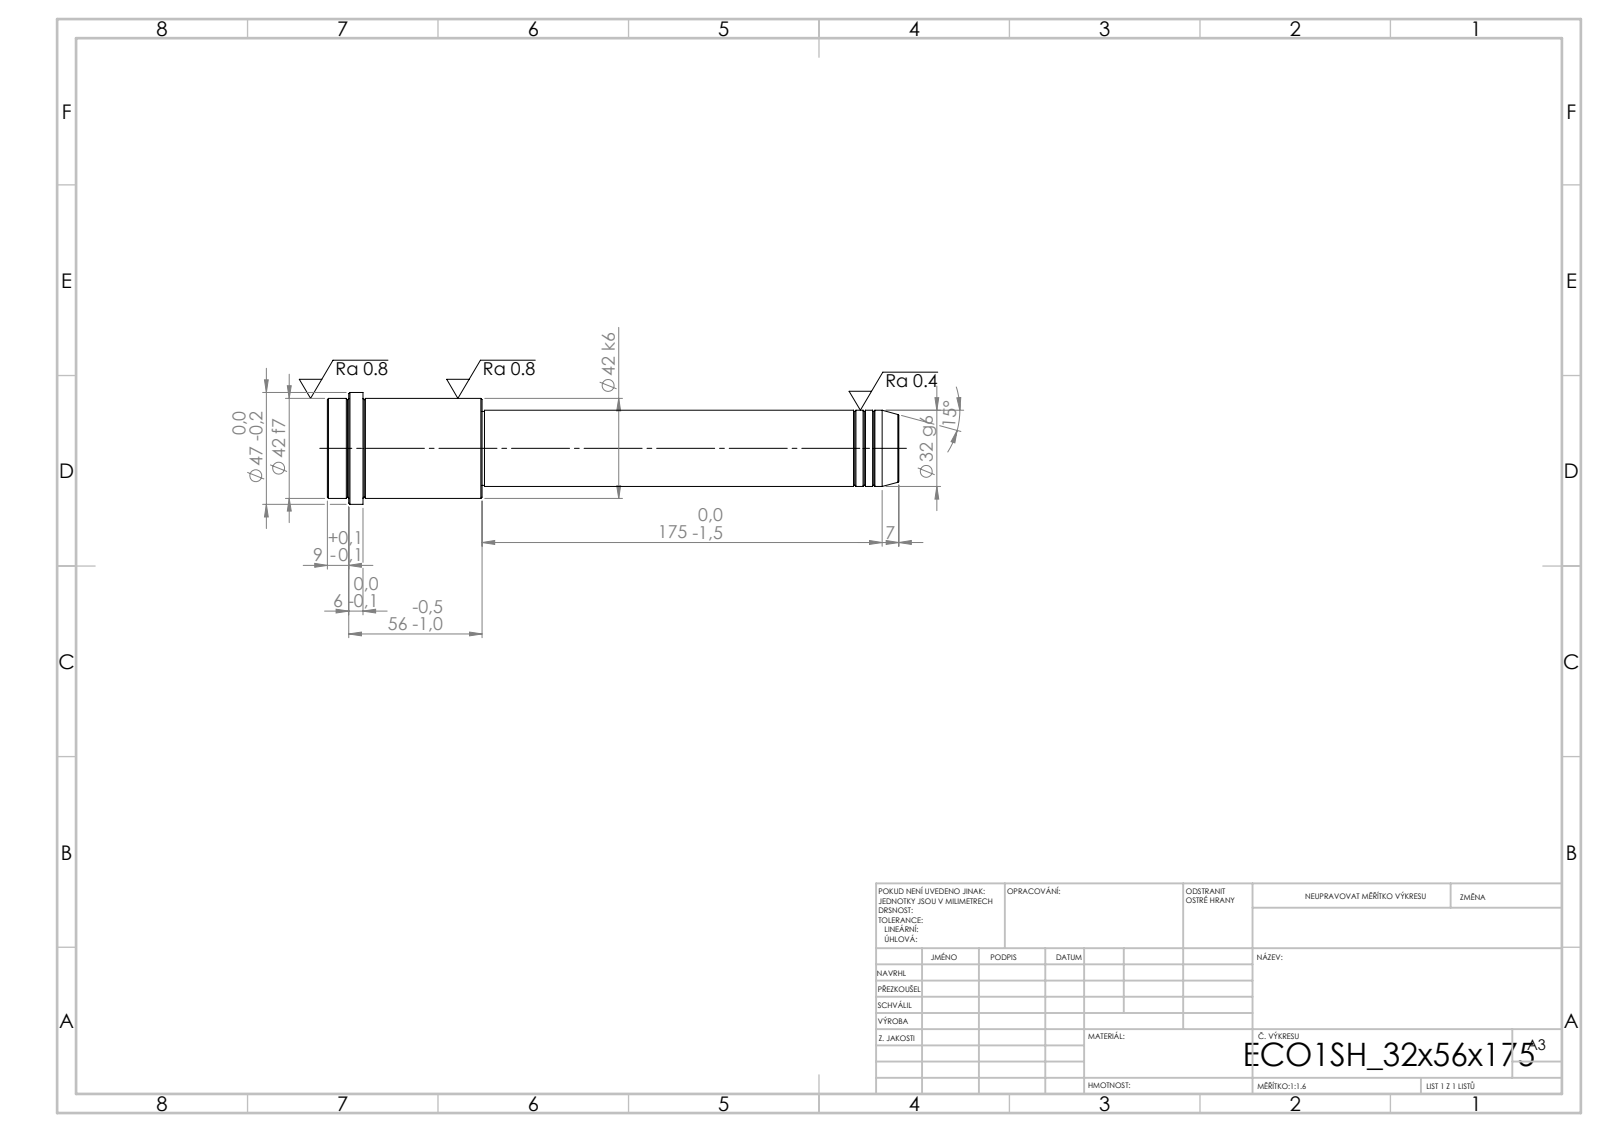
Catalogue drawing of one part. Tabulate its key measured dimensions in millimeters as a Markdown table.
| quantity | value |
| --- | --- |
| STEP written by | SolidWorks 2019 (CONFIG_CONTROL_DESIGN) |
| units | millimeters |
| bodies | 1 solid, 52 faces (6 planar, 16 cylindrical, 30 other) |
| overall size | 240 × 47 × 47 |
| volume | 231 937 mm³ |
| surface area | 29 810 mm² |
| round bosses / shafts (diameter × count) | 47 × 1, 42 × 1, 32 × 1, 31 × 1 |
| main face-to-face distances | 240, 175, 65, 225, 50, 15, 231, 56, 6, 9 |
